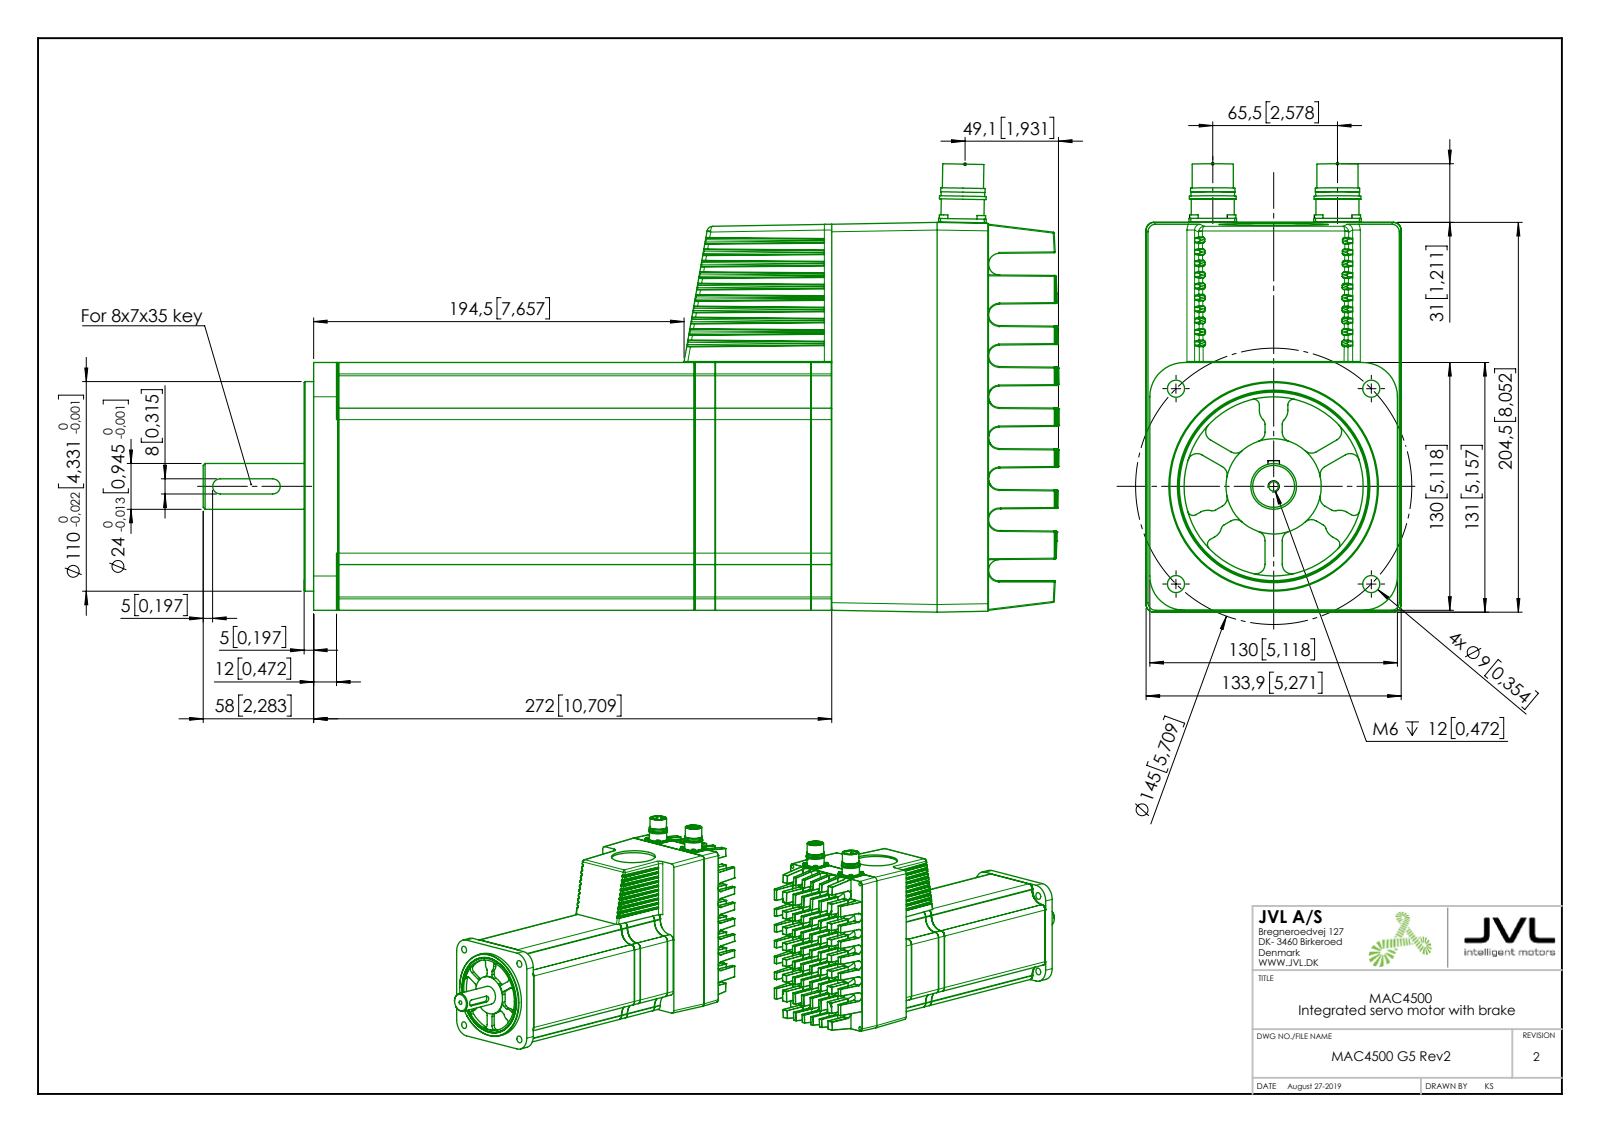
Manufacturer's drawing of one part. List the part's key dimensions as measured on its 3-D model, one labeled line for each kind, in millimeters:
Part name (STEP PRODUCT): Rear flange S; Module s; Brake part S; M23 male (+8 more)
STEP written by: SolidWorks 2018 (AUTOMOTIVE_DESIGN)
Units: millimetres
Bodies: 12 solids, 2547 faces (811 planar, 1007 cylindrical, 729 other)
Overall size (bounding box): 449.28 × 235.27 × 133.88
Volume: 6 925 000 mm³ · Surface area: 601 247 mm²
Round holes (diameter × count): ⌀2.5 ×8, ⌀2 ×5, ⌀4.3 ×4, ⌀9 ×4, ⌀20 ×2, ⌀20.2 ×2, ⌀4.6 ×1, ⌀5 ×1, ⌀57.62 ×1, ⌀94 ×1, ⌀100 ×1, ⌀117 ×1
Round bosses / shafts (diameter × count): ⌀4.5 ×8, ⌀2 ×5, ⌀24.5 ×2, ⌀23.3 ×2, ⌀22.9 ×2, ⌀22.6 ×2, ⌀21.6 ×2, ⌀112 ×1
Partial cylindrical surfaces — rounded edges, fillets, slot ends (radius × count): R0.5 ×297, R0.3 ×92, R0.8 ×40, R5 ×18, R3 ×15, R4 ×12, R0.6 ×10, R6 ×8
Main face-to-face distances: 61, 11, 130, 55.3, 116.3, 50, 66.3, 187, 198, 248
Hole centre spacings: 14.14, 20, 65.48, 7.05, 28.28, 56.37, 68.47, 72.51
